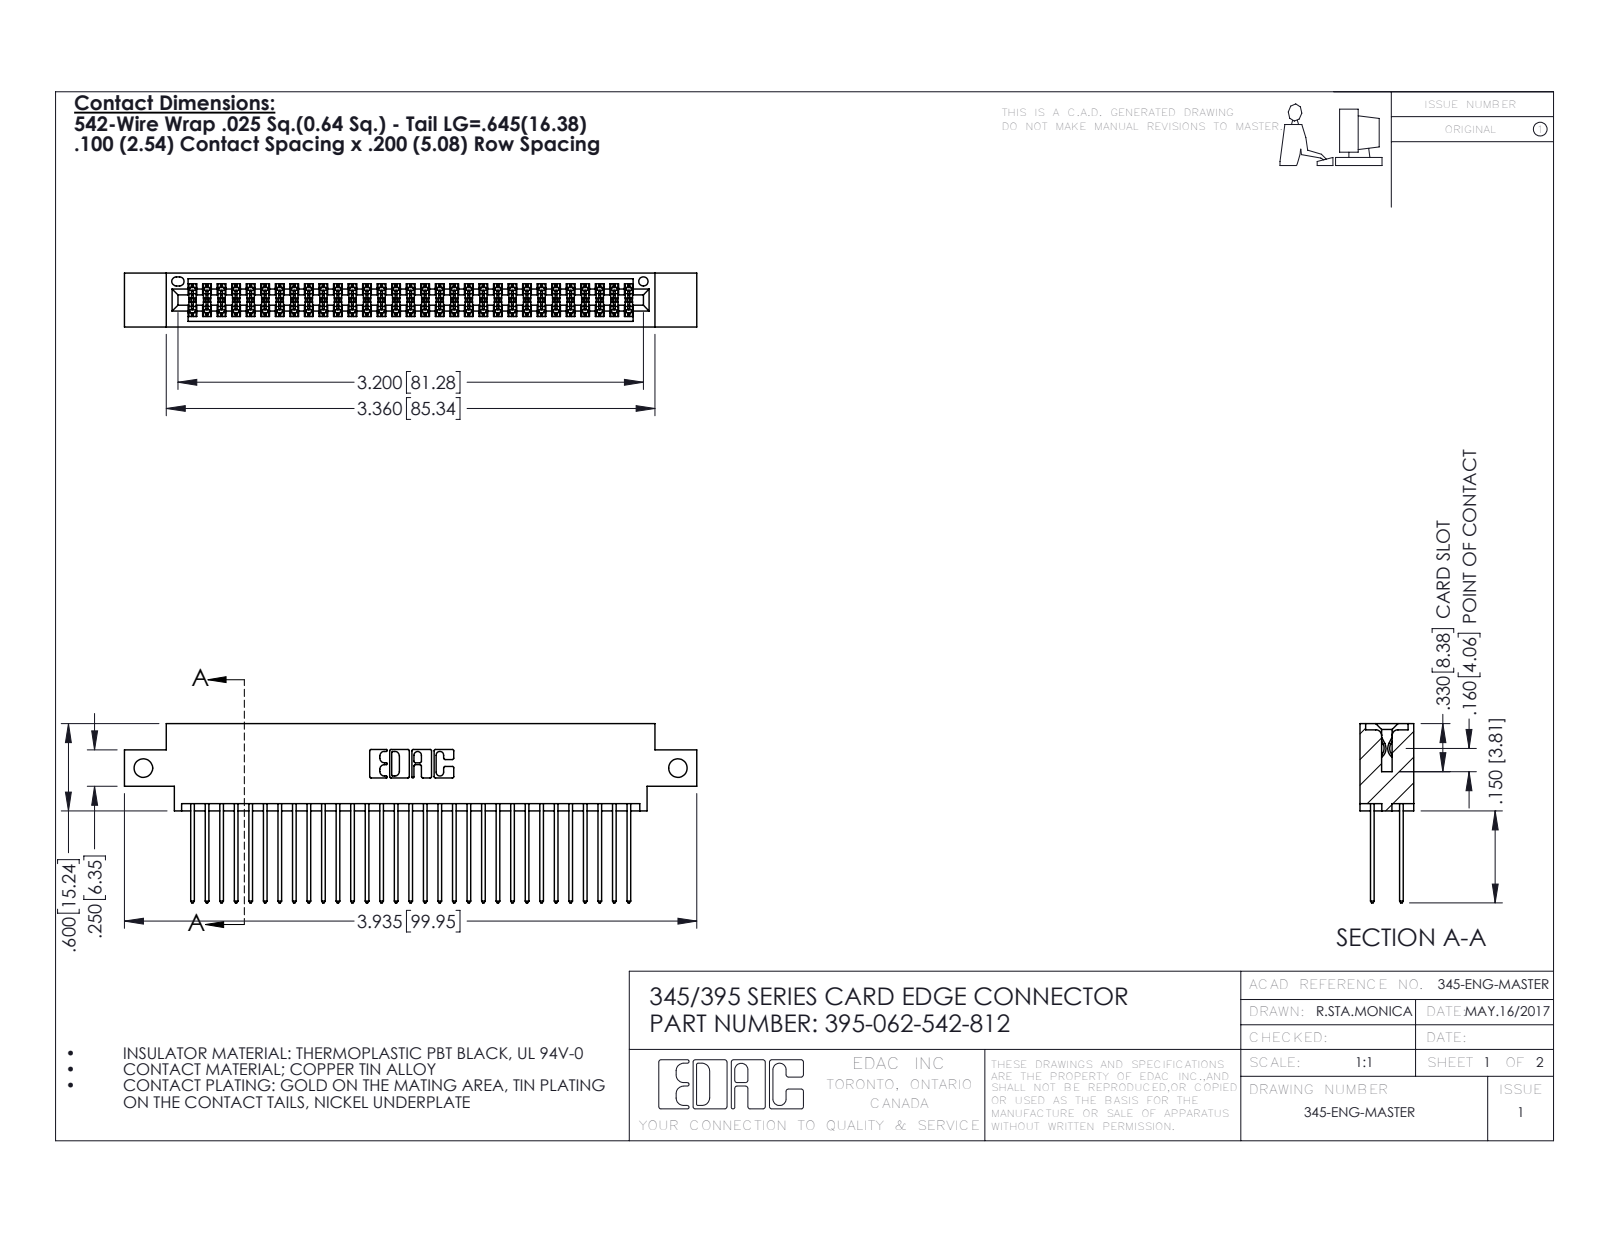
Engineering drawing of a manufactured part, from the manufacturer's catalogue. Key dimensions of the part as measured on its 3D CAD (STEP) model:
Part name (STEP PRODUCT): 345 Part_0.170 Offset - Side Mount; 395-062-542-812; 345-292-001_345-293-142
STEP written by: SolidWorks 2016 (CONFIG_CONTROL_DESIGN)
Units: inches
Bodies: 63 solids, 3230 faces (2130 planar, 1100 cylindrical, 0 other)
Overall size (bounding box): 3.935 × 1.232 × 0.37
Volume: 0.592 in³ · Surface area: 23.99 in²
Round holes (diameter × count): ⌀0.128 ×2, ⌀0.064 ×1
Partial cylindrical surfaces — rounded edges, fillets, slot ends (radius × count): R0.006 ×93, R0.01 ×62, R0.01 ×22, R0.007 ×6, R0.031 ×6, R0.026 ×3, R0.014 ×2, R0.019 ×2
Main face-to-face distances: 0.298, 0.072, 0.2, 0.098, 0.272, 0.025, 0.37, 0.225, 0.175, 0.149
Hole centre spacings: 3.675
